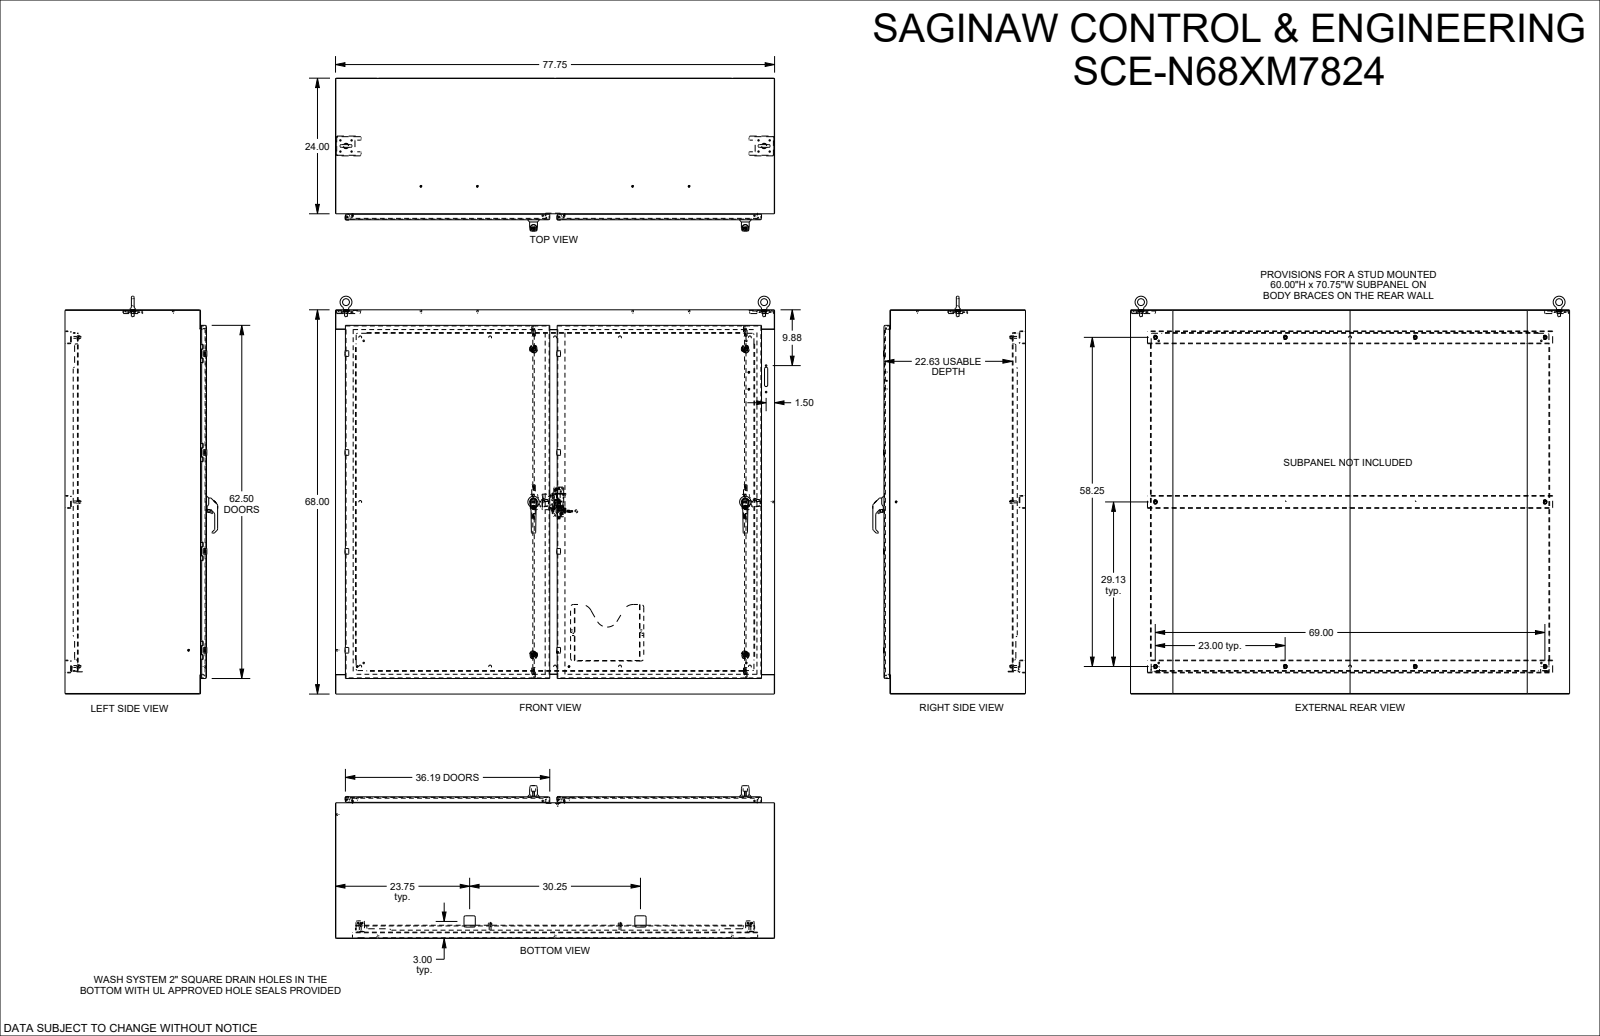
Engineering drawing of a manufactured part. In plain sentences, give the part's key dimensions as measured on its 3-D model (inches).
The part is named "SCE-N68XM7824". Its 3-D file was written by "SolidWorks 2023 (AUTOMOTIVE_DESIGN)". It is 47 solids with 7299 faces: 3034 planar, 2453 cylindrical and 1812 other. Overall it measures 77.75 by 70.945 by 27.046 inches. Its volume is 2 160 cubic inches and its surface area 41 159 square inches. Round holes: 16 of diameter 0.205, 16 of diameter 0.244, 14 of diameter 0.25, 8 of diameter 0.04, 8 of diameter 0.17, 8 of diameter 0.218, 8 of diameter 0.375, 8 of diameter 0.375, 4 of diameter 0.115, 4 of diameter 0.256, 4 of diameter 0.343, 4 of diameter 0.344. Round bosses or shafts: 24 of diameter 0.17, 19 of diameter 0.25, 16 of diameter 0.24, 10 of diameter 0.196, 4 of diameter 1.4, 4 of diameter 0.341, 2 of diameter 2.008, 2 of diameter 1.173. Partial cylindrical surfaces (rounded edges, fillets, slot ends): 208 of radius 0.03, 162 of radius 0.015, 66 of radius 0.125, 65 of radius 0.02, 57 of radius 0.04, 52 of radius 0.062, 48 of radius 0.02, 43 of radius 0.25. The main face-to-face distances are 0.104, 24.954, 24.85, 25.058, 67.896, 77.646, 23.896, 1.058, 68, 67.792. The hole center spacings are 17.5, 35, 37.5, 31.771, 0.984, 1.399, 1.4, 1.548.
